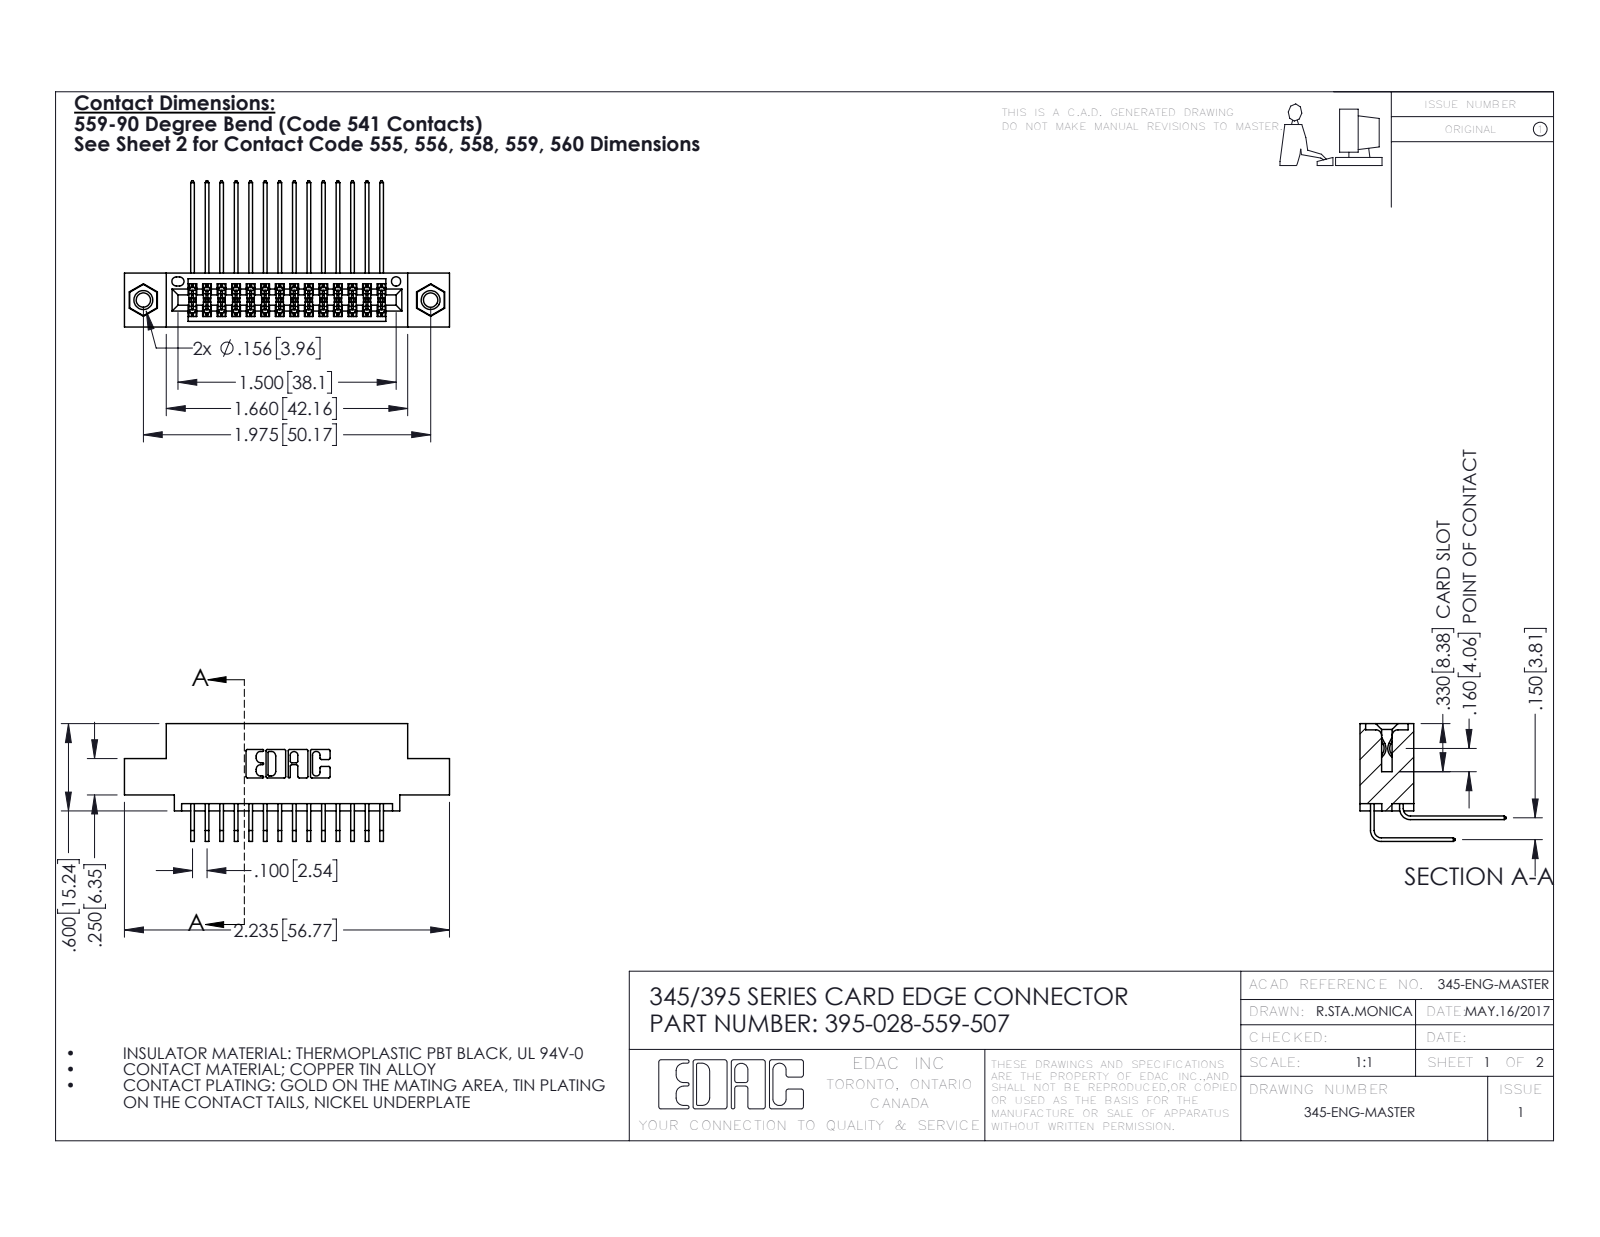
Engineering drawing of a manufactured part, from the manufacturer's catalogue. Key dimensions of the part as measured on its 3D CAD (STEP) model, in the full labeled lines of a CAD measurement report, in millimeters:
Part name (STEP PRODUCT): 345-292-001_559 Tail - 2; 345-250-001_345-250-005-103; 345-292-001_558 559 Tail - 1; 395-028-559-507 (+1 more)
STEP written by: SolidWorks 2016 (CONFIG_CONTROL_DESIGN)
Units: millimetres
Bodies: 31 solids, 1646 faces (1096 planar, 534 cylindrical, 16 other)
Overall size (bounding box): 56.8 × 25.5 × 20.5
Volume: 5 330 mm³ · Surface area: 8 213 mm²
Round holes (diameter × count): ⌀2.5 ×2, ⌀3.2 ×2, ⌀4 ×2, ⌀1.6 ×1
Round bosses / shafts (diameter × count): ⌀3.9 ×2
Partial cylindrical surfaces — rounded edges, fillets, slot ends (radius × count): R0.2 ×42, R0.3 ×22, R0.2 ×6, R0.8 ×6, R0.7 ×3, R0.4 ×2, R0.5 ×2, R0.6 ×2
Main face-to-face distances: 1.8, 7.6, 5.1, 9.4, 2.5, 6.9, 0.6, 5.7, 3.8, 4.4
Hole centre spacings: 6.9, 44.2, 50.2
